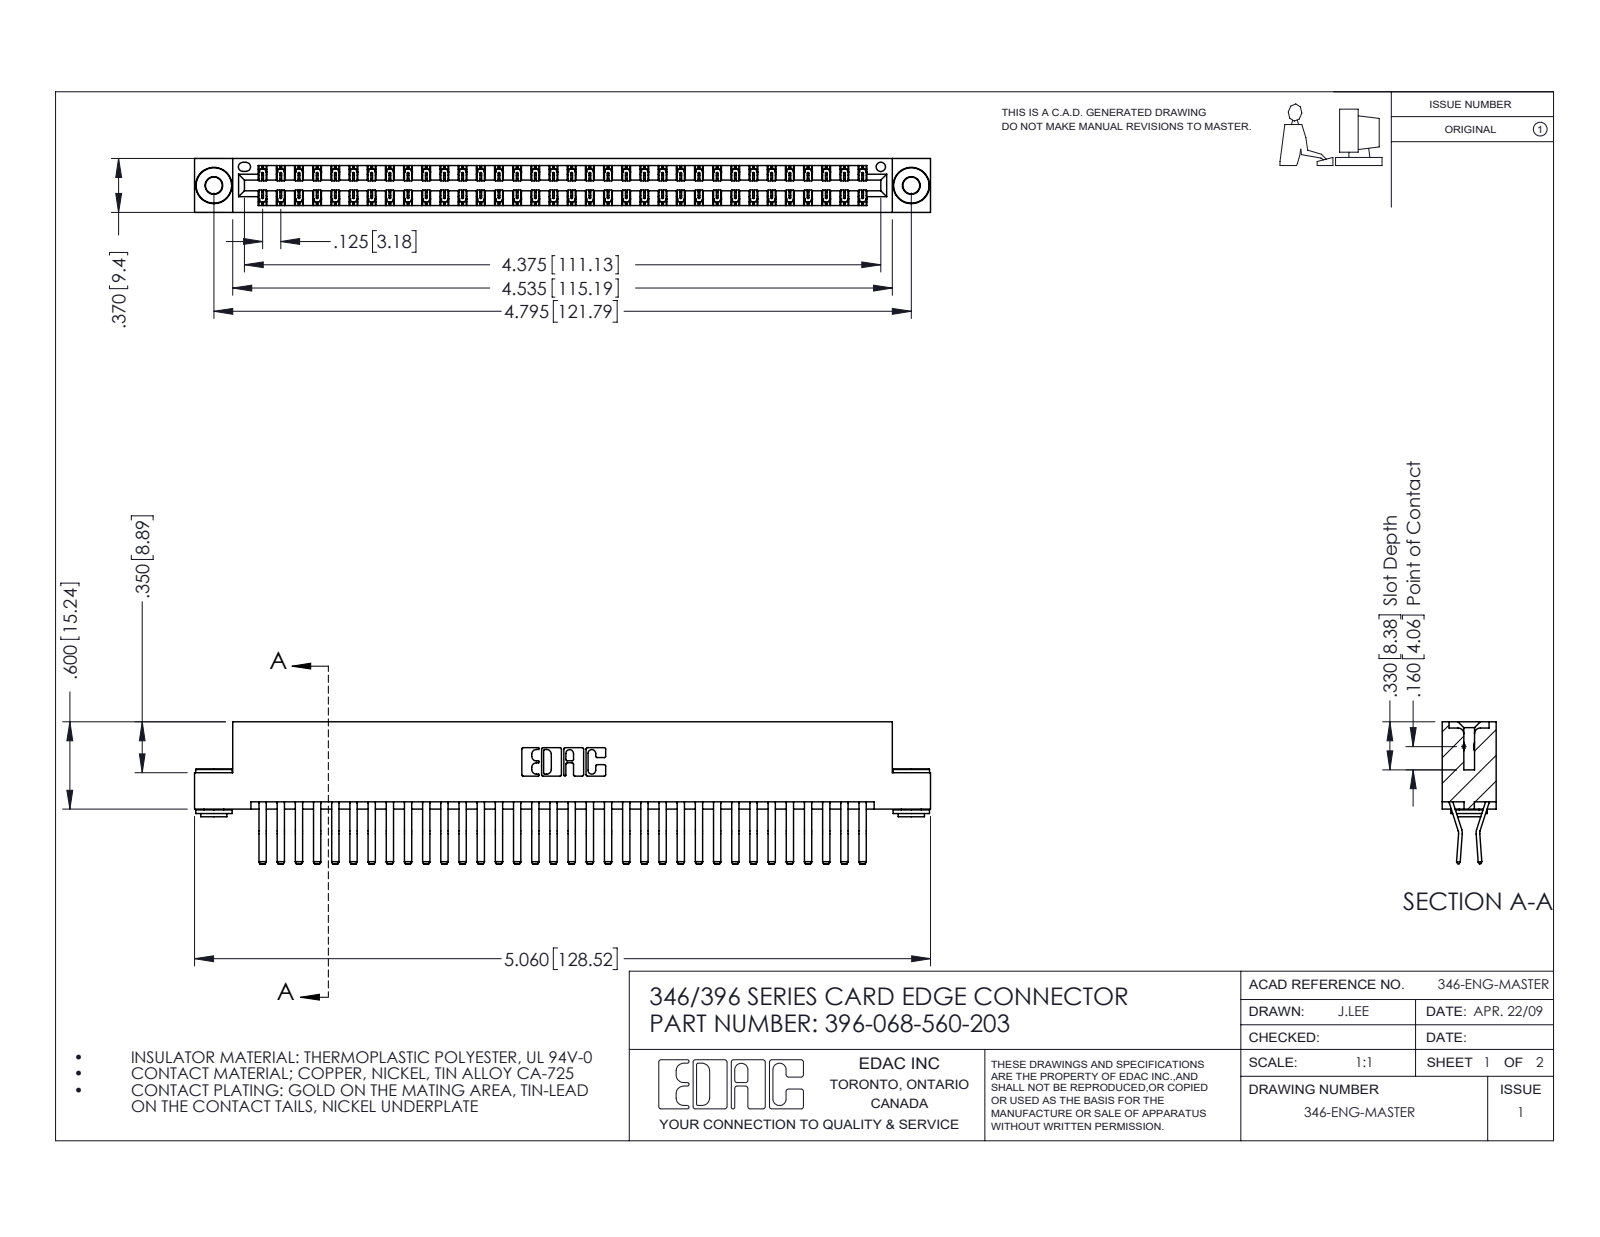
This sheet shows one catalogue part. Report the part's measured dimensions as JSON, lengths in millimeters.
{"part_name": "396-068-560-203; 346 Part_Flush Mounting Lugs - 0.156 Dia-TH; 345-292-001_560 Tail; 345-250-002_345-250-002-102", "step_written_by": "SolidWorks 2016 (CONFIG_CONTROL_DESIGN)", "units": "millimeters", "bodies": {"solids": 71, "faces": 3832, "planar": 2466, "cylindrical": 1358, "other": 8}, "overall_size": [128.5, 24.8, 9.4], "volume_mm3": 12900, "surface_area_mm2": 19060, "round_holes": [[2.9, 2], [4, 2], [1.6, 1]], "round_bosses_or_shafts": [[6.4, 2], [4.6, 2], [3.5, 2]], "partial_cylinders_radius": [[0.2, 102], [0.3, 22], [0.2, 6], [0.8, 6], [0.7, 3], [0.3, 2], [0.4, 2], [0.6, 2]], "face_to_face_distances": [1.2, 8.2, 9.4, 6.4, 0.6, 1.8, 7.6, 7, 3.8, 5.6], "hole_center_spacings": [6.2, 116.5, 121.8]}
